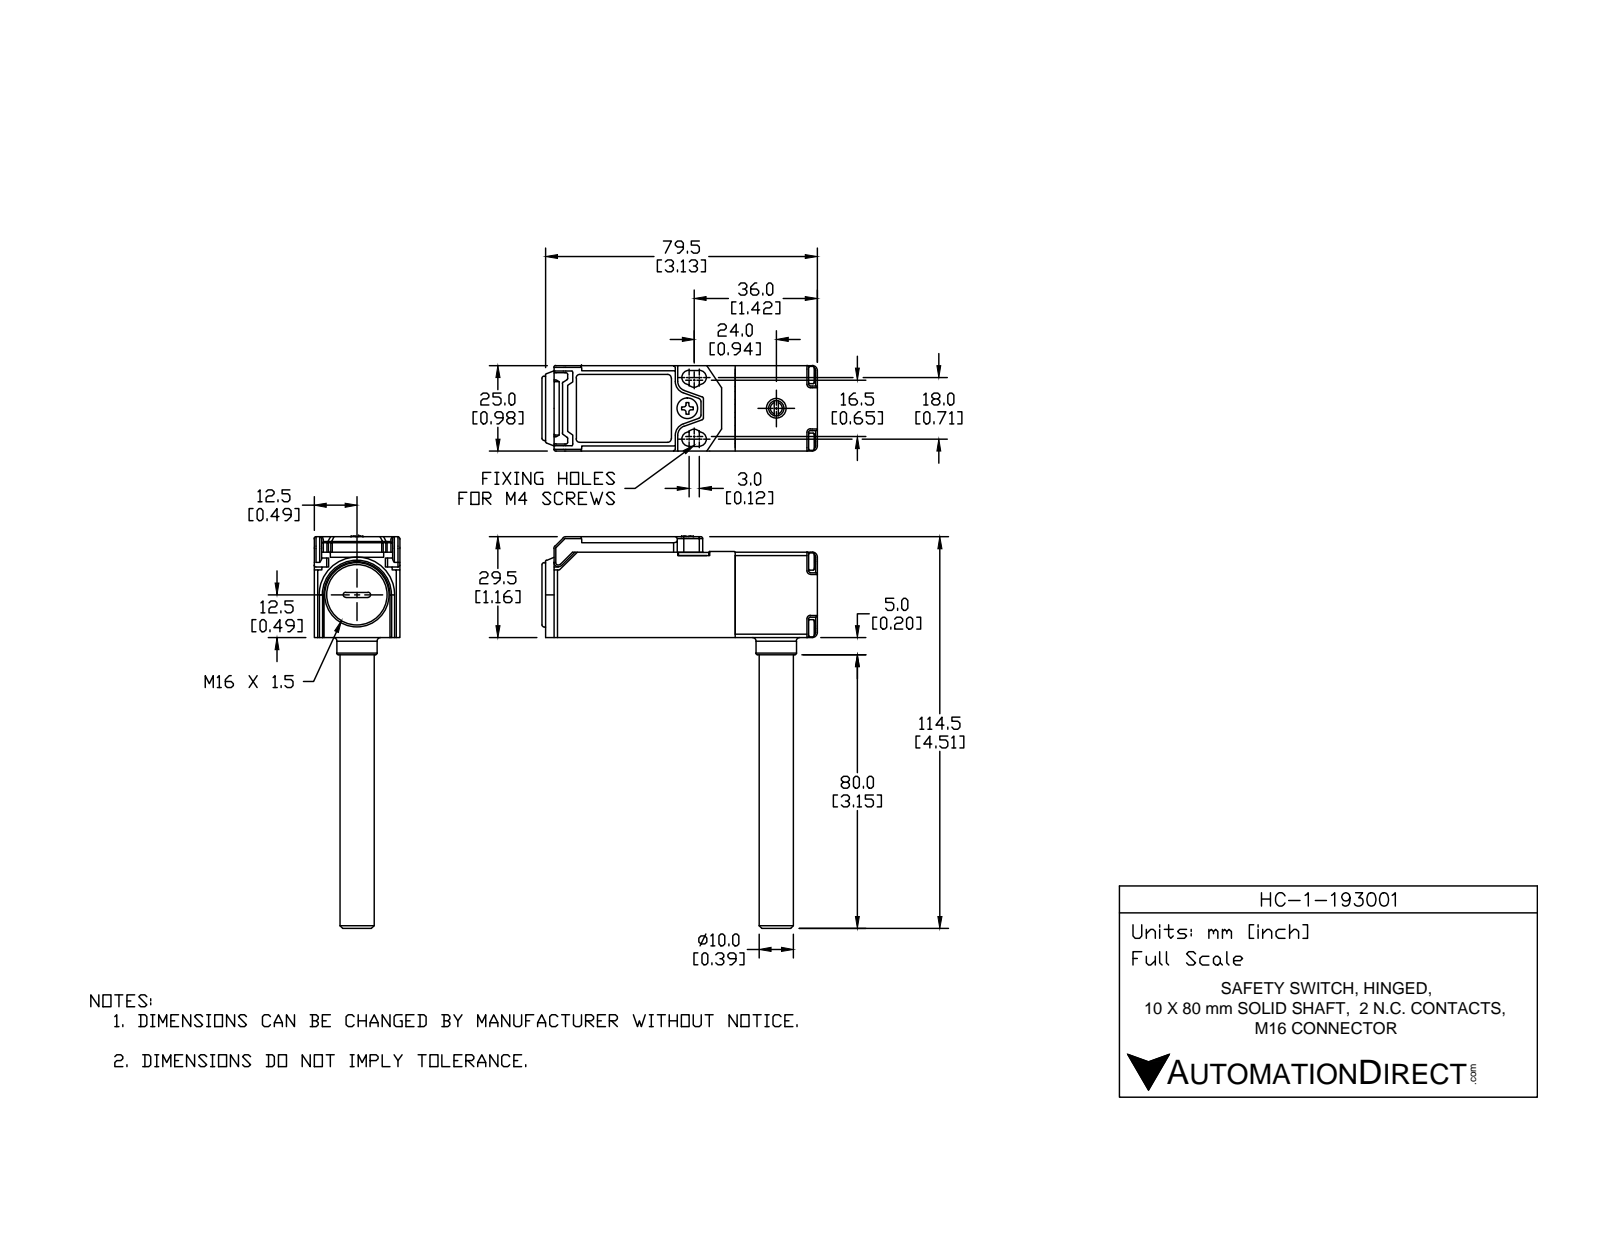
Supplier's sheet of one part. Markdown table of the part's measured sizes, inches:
| quantity | value |
| --- | --- |
| part name | HC-1-193001 |
| STEP written by | SolidWorks 2014 (AUTOMOTIVE_DESIGN) |
| units | inches |
| bodies | 14 solids, 1702 faces (700 planar, 601 cylindrical, 401 other) |
| overall size | 4.517 × 3.169 × 0.984 |
| volume | 1.932 in³ |
| surface area | 44.5 in² |
| round holes (diameter × count) | 0.126 × 5, 0.094 × 4, 0.059 × 2, 0.063 × 2, 0.071 × 2, 0.087 × 2, 0.142 × 2, 0.055 × 1, 0.081 × 1, 0.098 × 1, 0.102 × 1, 0.185 × 1 |
| round bosses / shafts (diameter × count) | 0.102 × 5, 0.197 × 4, 0.079 × 4, 0.138 × 2, 0.74 × 1, 0.531 × 1, 0.394 × 1, 0.386 × 1 |
| partial cylindrical surfaces (radius × count) | 0.02 × 226, 0.004 × 24, 0.012 × 20, 0.039 × 20, 0.059 × 7, 0.083 × 6, 0.11 × 6, 0.008 × 4 |
| main face-to-face distances | 0.984, 0.079, 0.071, 0.913, 0.039, 0.906, 0.945, 0.827, 0.874, 1.15 |
| hole center spacings | 0.543, 0.768, 0.171, 0.187, 0.245, 0.414, 0.423, 0.426 |
